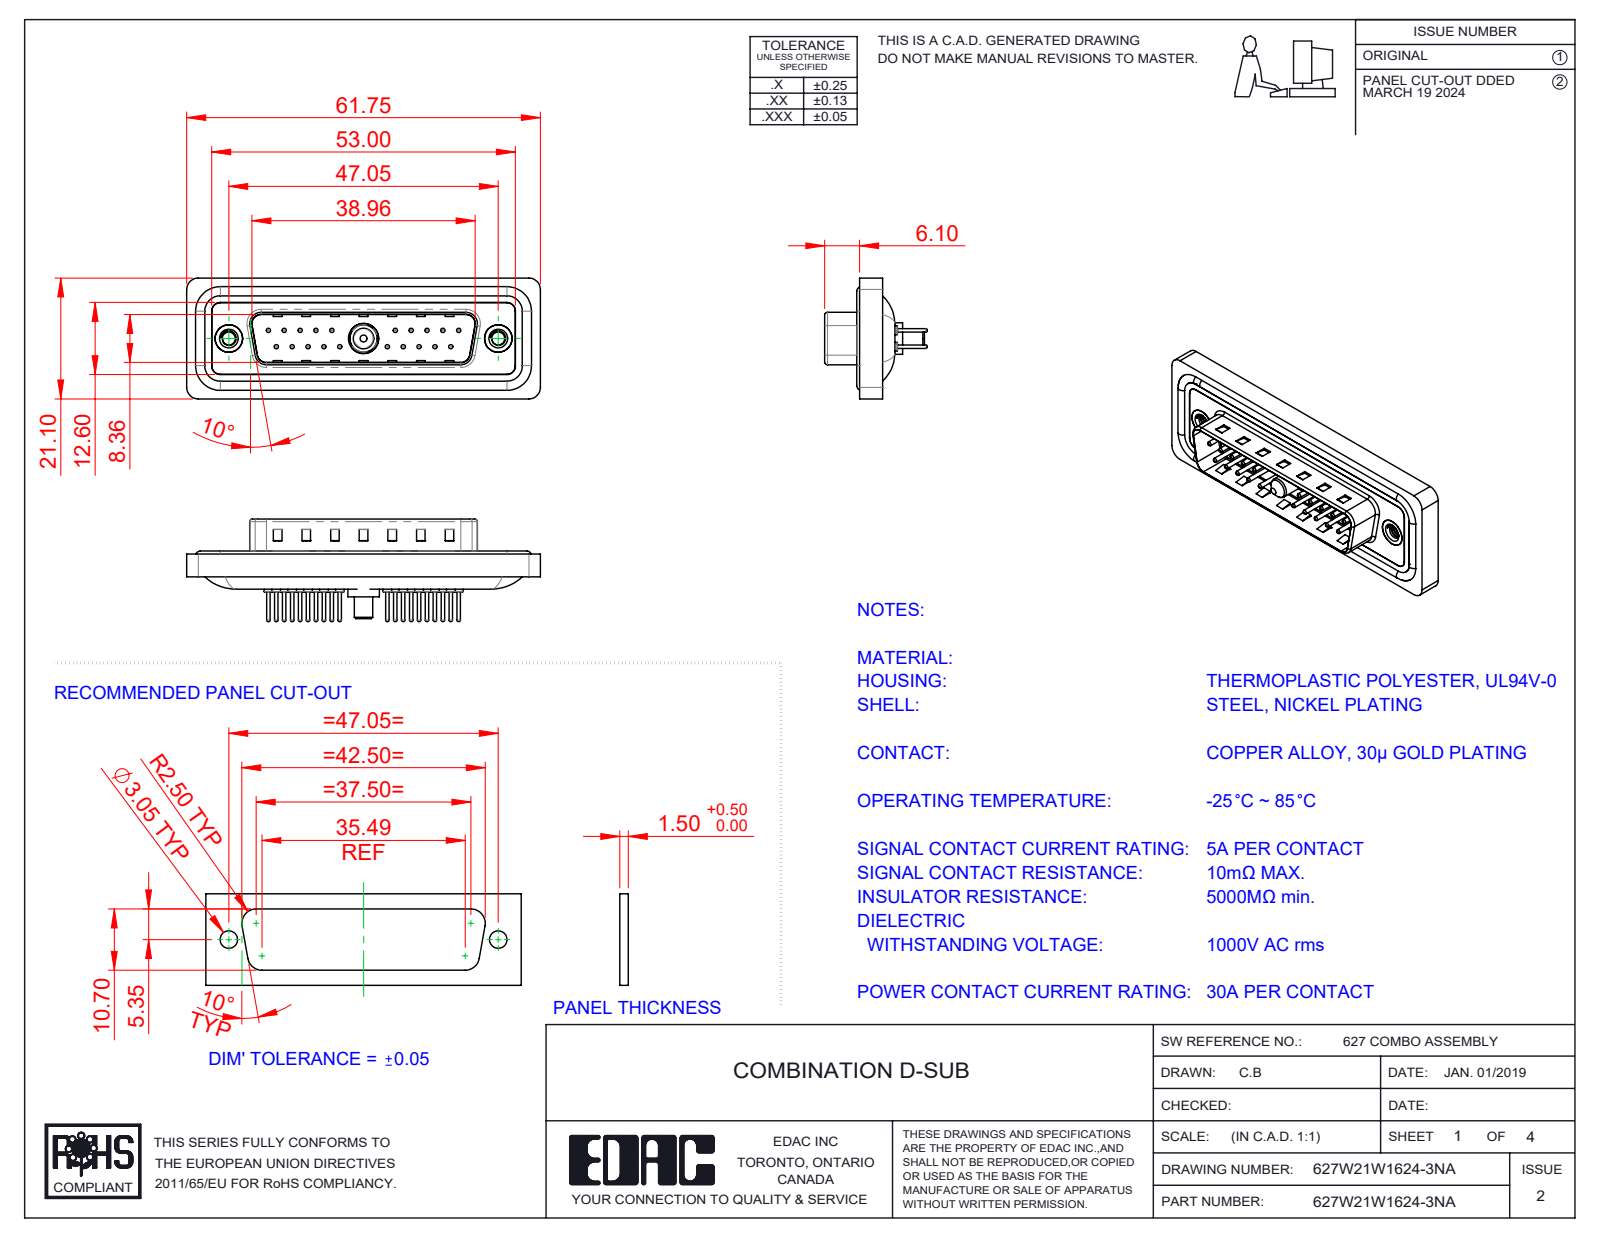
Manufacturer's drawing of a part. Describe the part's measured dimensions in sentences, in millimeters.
The part is named "627Combo Waterproof Housing_25 Contacts; 627Combo Housing_21W1; 627Combo Contact Row 1_24; 627Combo Shell Rear_25 Contacts (+5 more)". Its 3-D file was written by "SolidWorks 2023 (CONFIG_CONTROL_DESIGN)". It is 29 solids with 1260 faces: 359 planar, 489 cylindrical and 412 other. Overall it measures 61.75 by 21.1 by 17.9 millimeters. Its volume is 7 206 cubic millimeters and its surface area 11 955 square millimeters. Round holes: 20 of diameter 0.75, 20 of diameter 1.6, 20 of diameter 2, 2 of diameter 2.26, 2 of diameter 4, 2 of diameter 4.8, 2 of diameter 5, 1 of diameter 4.85, 1 of diameter 5.3. Round bosses or shafts: 20 of diameter 1.5, 20 of diameter 0.6, 4 of diameter 1.6, 2 of diameter 4.9, 1 of diameter 5.5, 1 of diameter 5.2, 1 of diameter 4.75, 1 of diameter 3.75. Partial cylindrical surfaces (rounded edges, fillets, slot ends): 22 of radius 1.5, 18 of radius 2, 8 of radius 0.5, 8 of radius 1.6, 4 of radius 0.25, 4 of radius 0.6, 4 of radius 0.65, 4 of radius 0.9. The main face-to-face distances are 0.4, 1.5, 1.1, 1.6, 0.5, 3.1, 2.9, 4.1, 0.82, 9.58. The hole center spacings are 3.16, 2.77, 5.54, 8.31, 5.04, 19.39, 20.97, 22.16.
